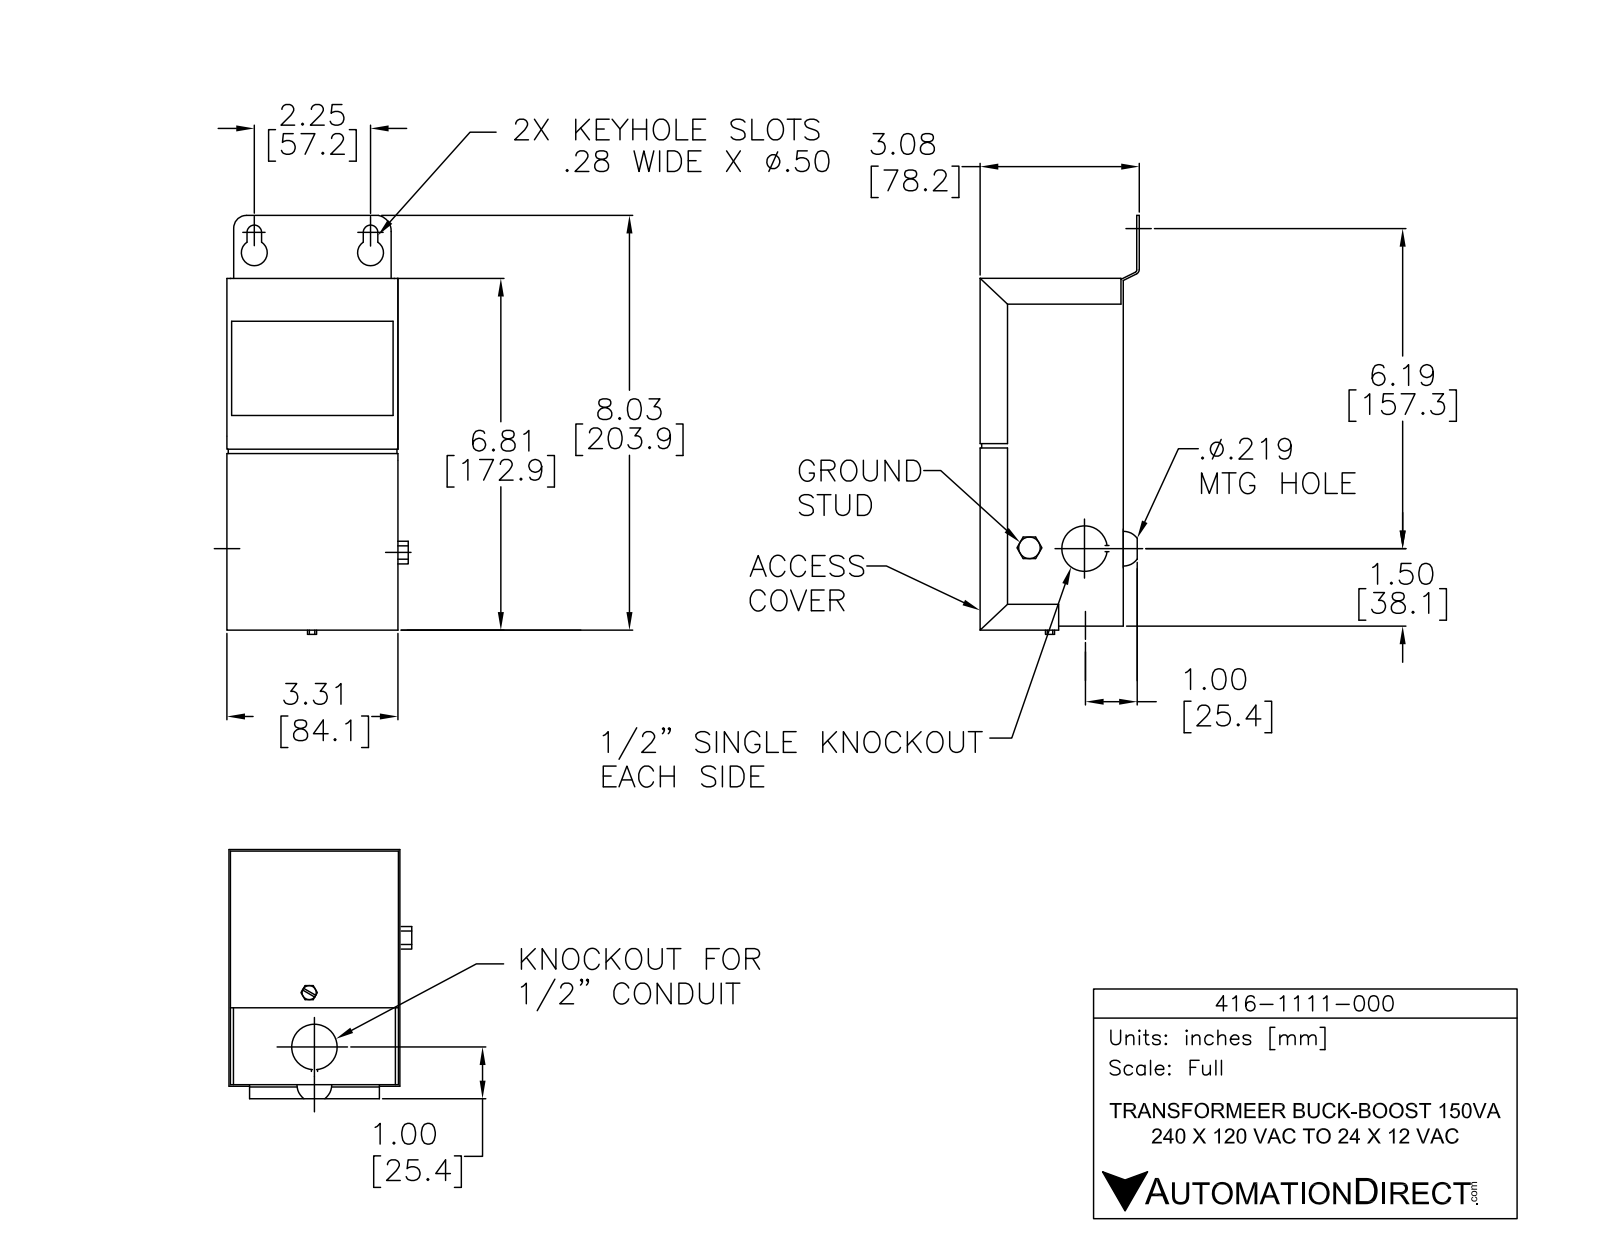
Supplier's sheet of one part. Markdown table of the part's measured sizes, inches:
| quantity | value |
| --- | --- |
| part name | 416-1111-000 |
| STEP written by | SolidWorks 2013 (AUTOMOTIVE_DESIGN) |
| units | inches |
| bodies | 1 solid, 150 faces (89 planar, 45 cylindrical, 16 other) |
| overall size | 8.14 × 3.42 × 3.081 |
| volume | 63.4 in³ |
| surface area | 112.7 in² |
| round holes (diameter × count) | 0.5 × 2, 0.875 × 2, 0.185 × 1, 0.231 × 1, 0.275 × 1 |
| partial cylindrical surfaces (radius × count) | 0.04 × 10, 0.25 × 10, 0.14 × 2, 0.06 × 1, 0.1 × 1 |
| main face-to-face distances | 2.861, 3.23, 0.04, 3.27, 0.04, 2.86, 3.31, 6.81, 6.77, 0.22 |
| hole center spacings | 5.908, 0.763, 0.862, 2.25 |
